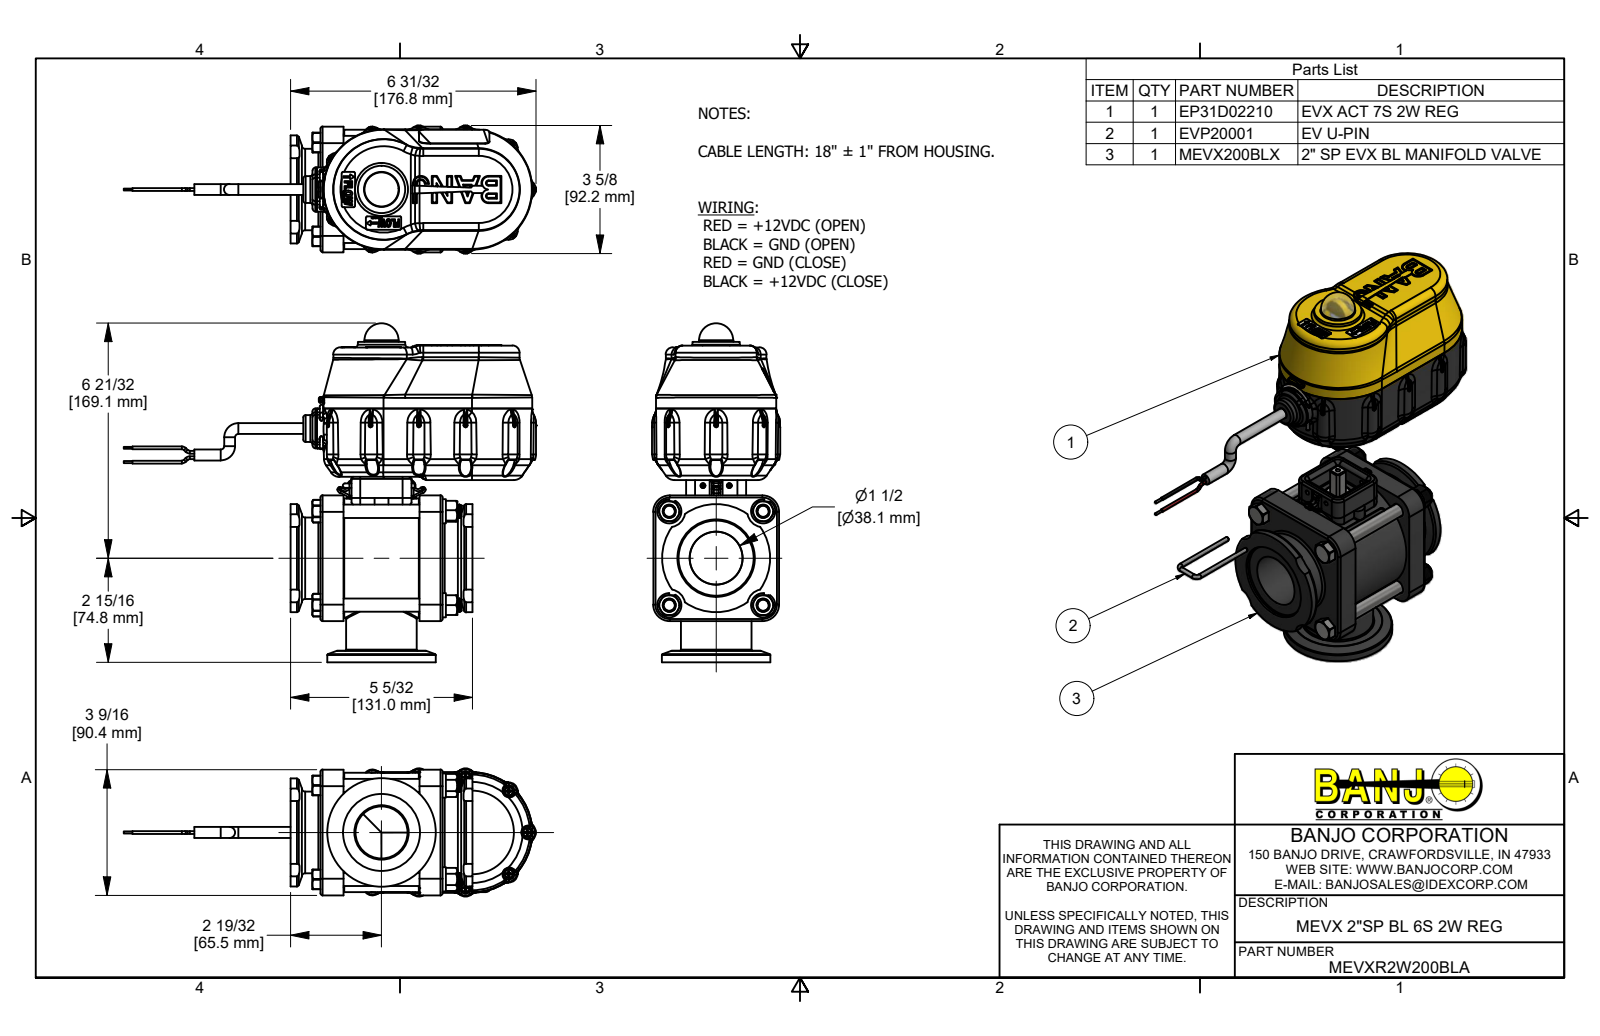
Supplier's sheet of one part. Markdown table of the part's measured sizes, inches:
| quantity | value |
| --- | --- |
| part name | MEVXR2W200BLA; EP31D02210; 91400A119; 95584A200 (+8 more) |
| STEP written by | Autodesk Inventor 2019 (AUTOMOTIVE_DESIGN) |
| units | inches |
| bodies | 97 solids, 12850 faces (3825 planar, 3310 cylindrical, 5715 other) |
| overall size | 11.685 × 9.602 × 3.63 |
| volume | 68.75 in³ |
| surface area | 662.7 in² |
| round holes (diameter × count) | 0.15 × 13, 0.095 × 11, 0.107 × 4, 0.126 × 4, 0.136 × 4, 0.17 × 4, 0.307 × 4, 0.385 × 4, 0.406 × 4, 1.5 × 3, 0.089 × 2, 0.105 × 2 |
| round bosses / shafts (diameter × count) | 0.324 × 60, 0.25 × 17, 0.14 × 11, 0.108 × 11, 0.085 × 11, 0.08 × 10, 0.375 × 5, 0.687 × 4 |
| partial cylindrical surfaces (radius × count) | 0.04 × 147, 0.02 × 91, 0.01 × 56, 0.005 × 43, 0.06 × 40, 0.08 × 28, 0.03 × 24, 0.015 × 22 |
| main face-to-face distances | 0.1, 2.565, 0.65, 2.808, 0.825, 2.633, 0.175, 1.983, 1.5, 0.85 |
| hole center spacings | 1.283, 1.88, 2.659, 2.73, 2.967, 3.45, 0.487, 0.492 |
